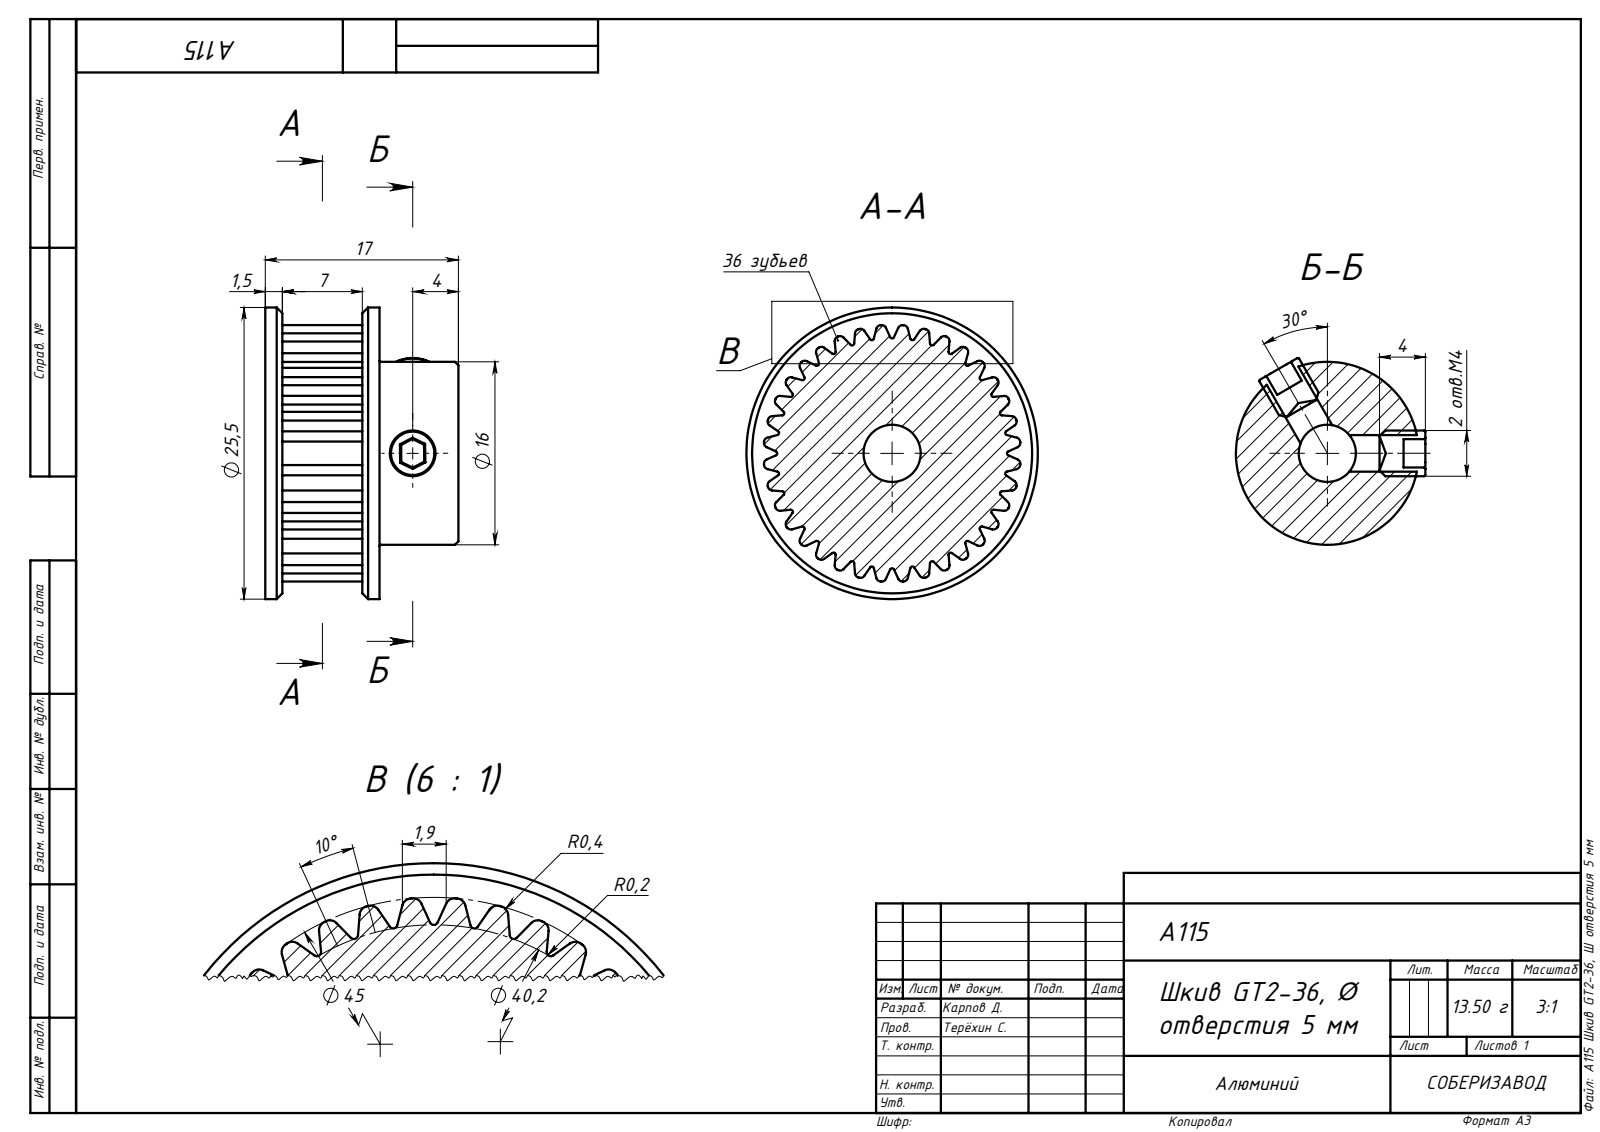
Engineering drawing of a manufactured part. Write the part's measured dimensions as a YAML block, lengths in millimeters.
part_name: "A115 Шкив GT2-36, O отверстия 5 мм"
step_written_by: "SolidWorks 2019 (AUTOMOTIVE_DESIGN)"
units: millimeters
bodies: {solids: 3, faces: 319, planar: 106, cylindrical: 189, other: 24}
overall_size: [25.5, 25.5, 17]
volume: 5116
surface_area: 3152
round_holes:
  - {diameter: 3.2, count: 2}
  - {diameter: 5, count: 1}
round_bosses_or_shafts:
  - {diameter: 4, count: 2}
  - {diameter: 25.5, count: 1}
  - {diameter: 16, count: 1}
partial_cylinders:
  - {radius: 0.4, count: 72}
  - {radius: 0.18, count: 36}
  - {radius: 11.25, count: 1}
face_to_face_distances: [10, 1.5, 8.5, 8.14, 10.1, 6.9, 16.9, 17, 8.4, 8.6]
